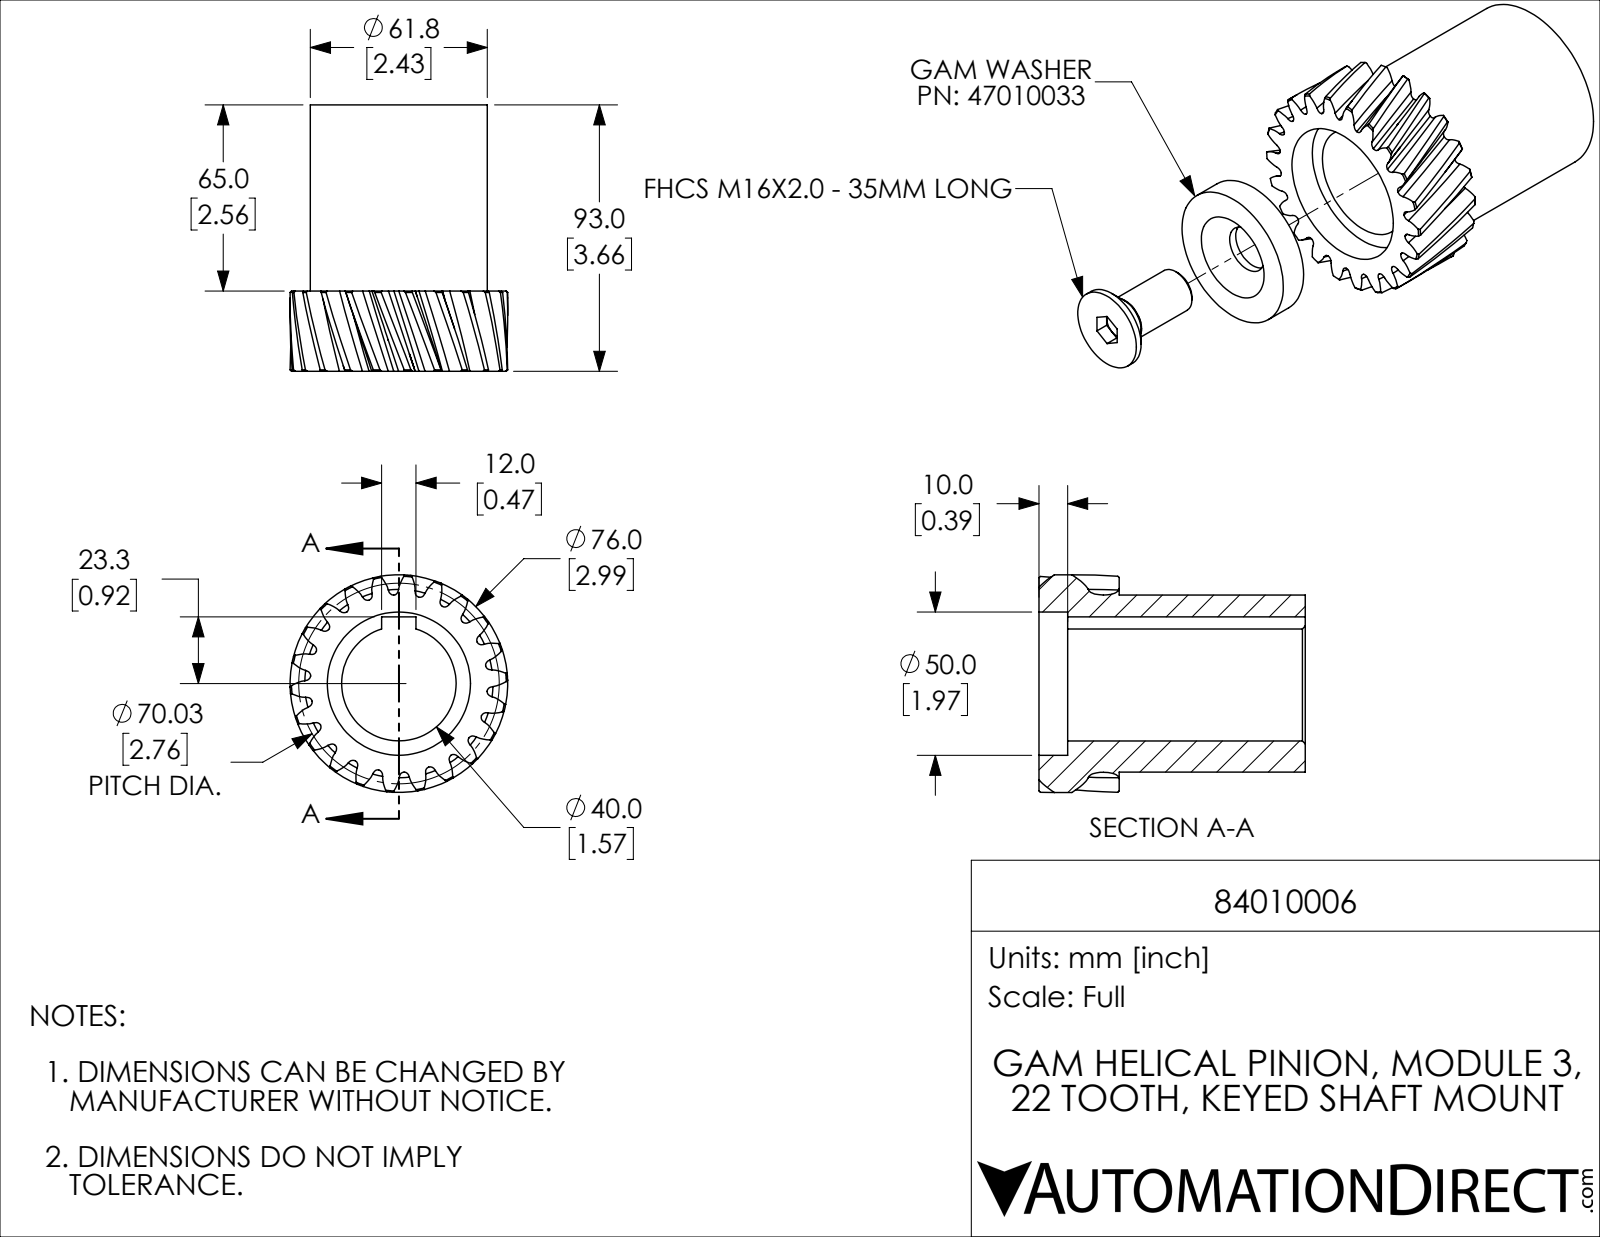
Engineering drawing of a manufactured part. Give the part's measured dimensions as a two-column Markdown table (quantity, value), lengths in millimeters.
| quantity | value |
| --- | --- |
| part name | 84010006 |
| STEP written by | SolidWorks 2019 (CONFIG_CONTROL_DESIGN) |
| units | millimeters |
| bodies | 3 solids, 205 faces (23 planar, 38 cylindrical, 144 other) |
| overall size | 93 × 76 × 76 |
| volume | 198 094 mm³ |
| surface area | 51 037 mm² |
| round holes (diameter × count) | 17 × 1, 40 × 1, 50 × 1 |
| round bosses / shafts (diameter × count) | 76 × 1, 61.8 × 1, 28.96 × 1, 16 × 1 |
| main face-to-face distances | 10, 93, 83, 28, 18, 65, 12, 35, 25, 7 |
